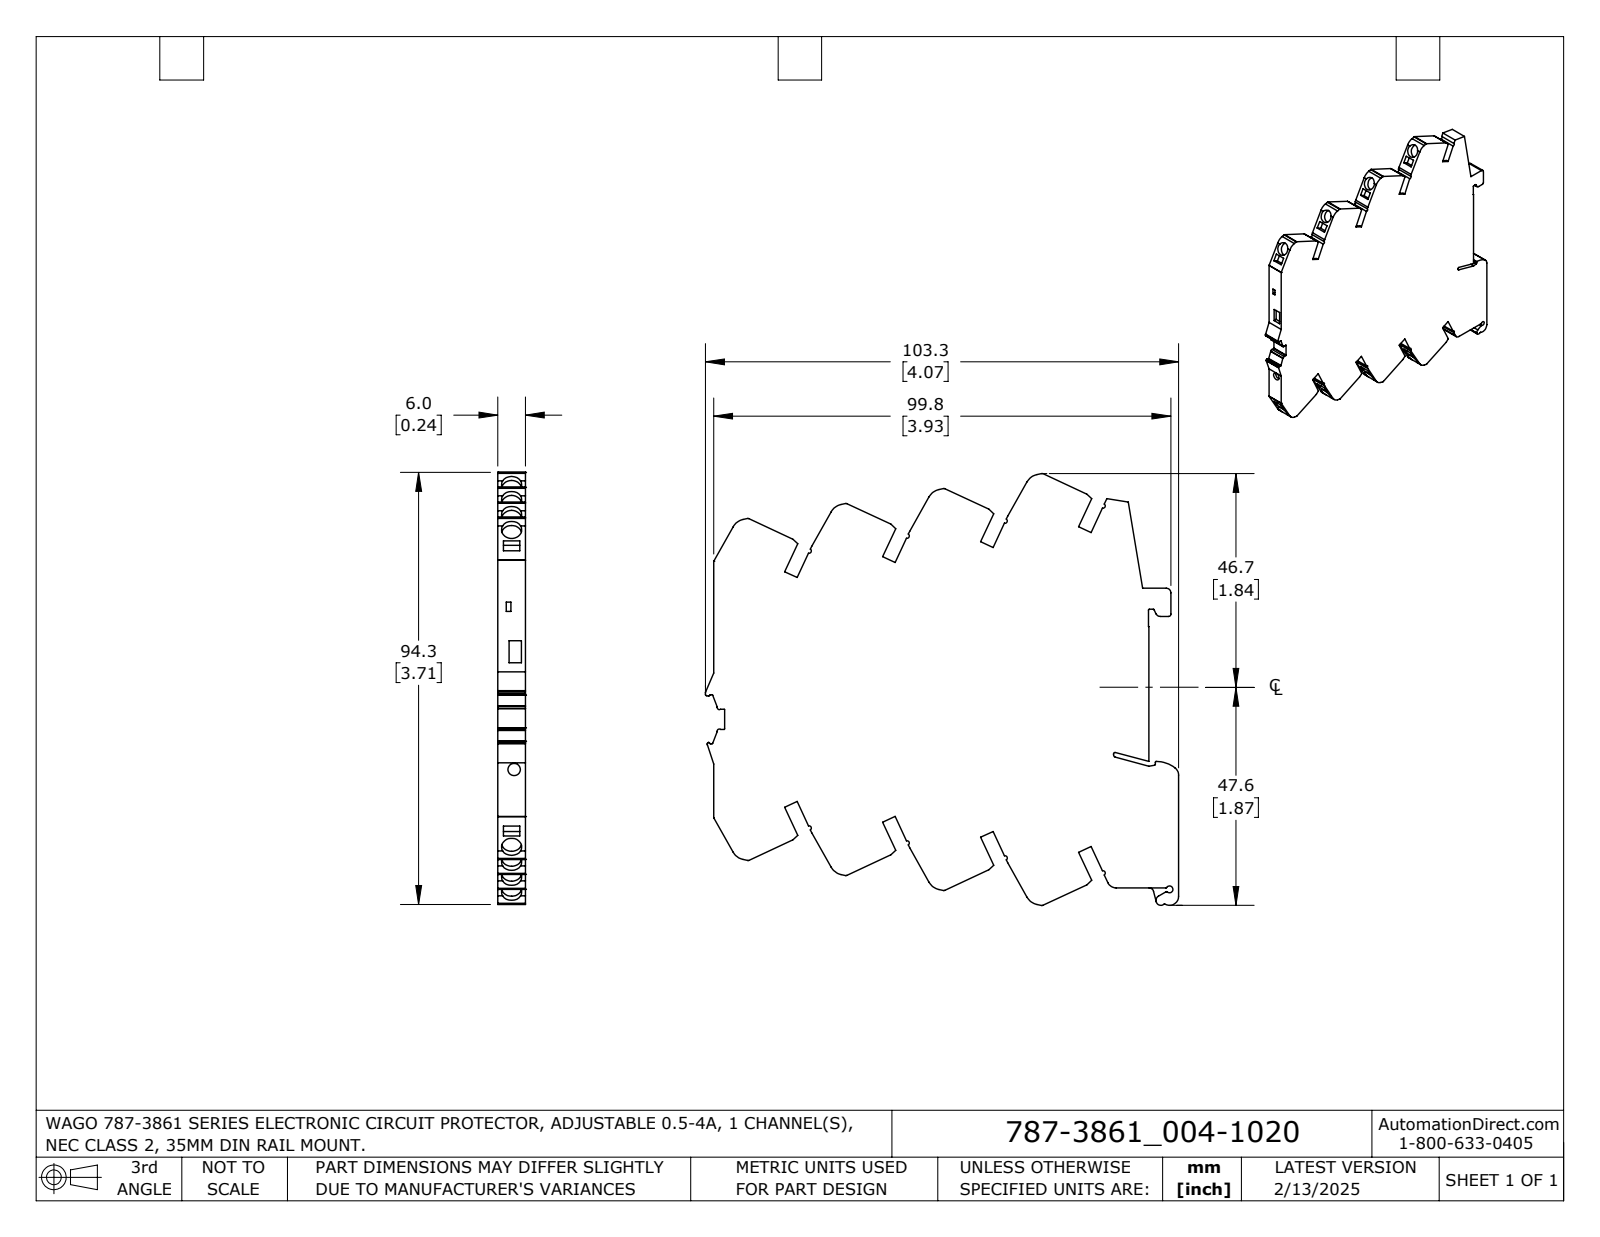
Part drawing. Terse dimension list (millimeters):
name: 787-3861_004-1020_HI
written by: SolidWorks 2024 (AUTOMOTIVE_DESIGN)
unit: mm
bodies: 1 solid, 267 faces (202 planar, 65 cylindrical, 0 other)
size: 103.3 × 94.26 × 6
volume: 43 980 mm³; area: 18 879 mm²
holes: 8× ⌀4.4, 1× ⌀2.7
rounds: 13× R0.2, 12× R0.5, 8× R0.4, 8× R3.35, 5× R1, 3× R0.3, 3× R2, 2× R0.45
face distances: 6, 17.99, 17.02, 12.01, 3, 35.98, 12, 24.01, 14.99, 34.04
hole spacings: 13.35, 13.34, 26.7, 26.71, 40.05
